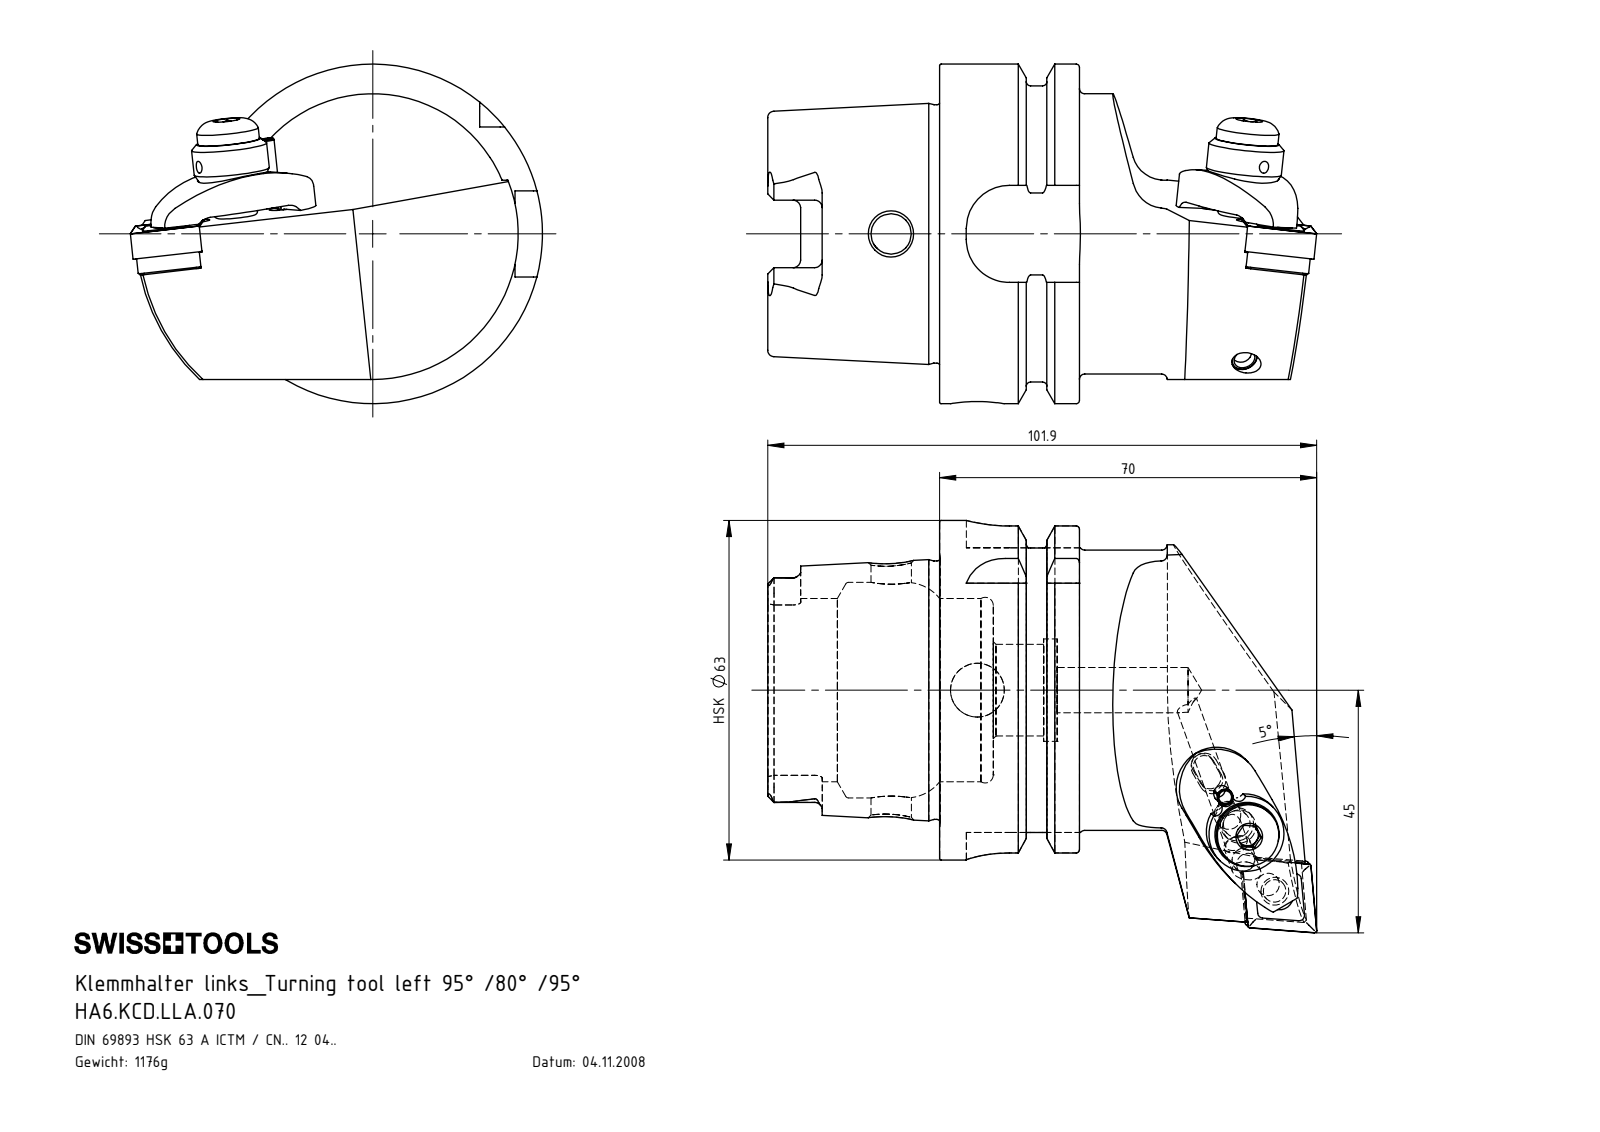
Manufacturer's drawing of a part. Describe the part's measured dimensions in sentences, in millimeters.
The part is named "HA6.KCD.LLA.070; ISO 13337 - 3 x 12_PreviewCfg; WCC-ER4.103.032_A; WCC-ER5.102.012_B (+7 more)". Its 3-D file was written by "SolidWorks 2017 (AUTOMOTIVE_DESIGN)". It is 11 solids with 470 faces: 125 planar, 153 cylindrical and 192 other. Overall it measures 101.9 by 76.5 by 63 millimeters. Its volume is 148 969 cubic millimeters and its surface area 35 490 square millimeters. Round holes: 3 of diameter 2, 3 of diameter 4.2, 2 of diameter 5, 2 of diameter 7, 1 of diameter 2.4, 1 of diameter 3, 1 of diameter 4, 1 of diameter 5.16, 1 of diameter 6.2, 1 of diameter 6.4, 1 of diameter 7.5, 1 of diameter 8.4. Round bosses or shafts: 2 of diameter 5, 2 of diameter 3, 1 of diameter 63, 1 of diameter 54.95, 1 of diameter 52, 1 of diameter 47.94, 1 of diameter 14, 1 of diameter 11.5. Partial cylindrical surfaces (rounded edges, fillets, slot ends): 6 of radius 0.39, 6 of radius 1.4, 4 of radius 0.4, 4 of radius 1, 4 of radius 8, 3 of radius 0.69, 3 of radius 0.69, 3 of radius 1.5. The main face-to-face distances are 25.95, 16, 9.95, 31.9, 41.85, 57.85, 52.8, 21.8, 11.85, 53.7. The hole center spacings are 8, 7.28, 8.2, 15, 15.11, 22.94, 23, 7.09.
